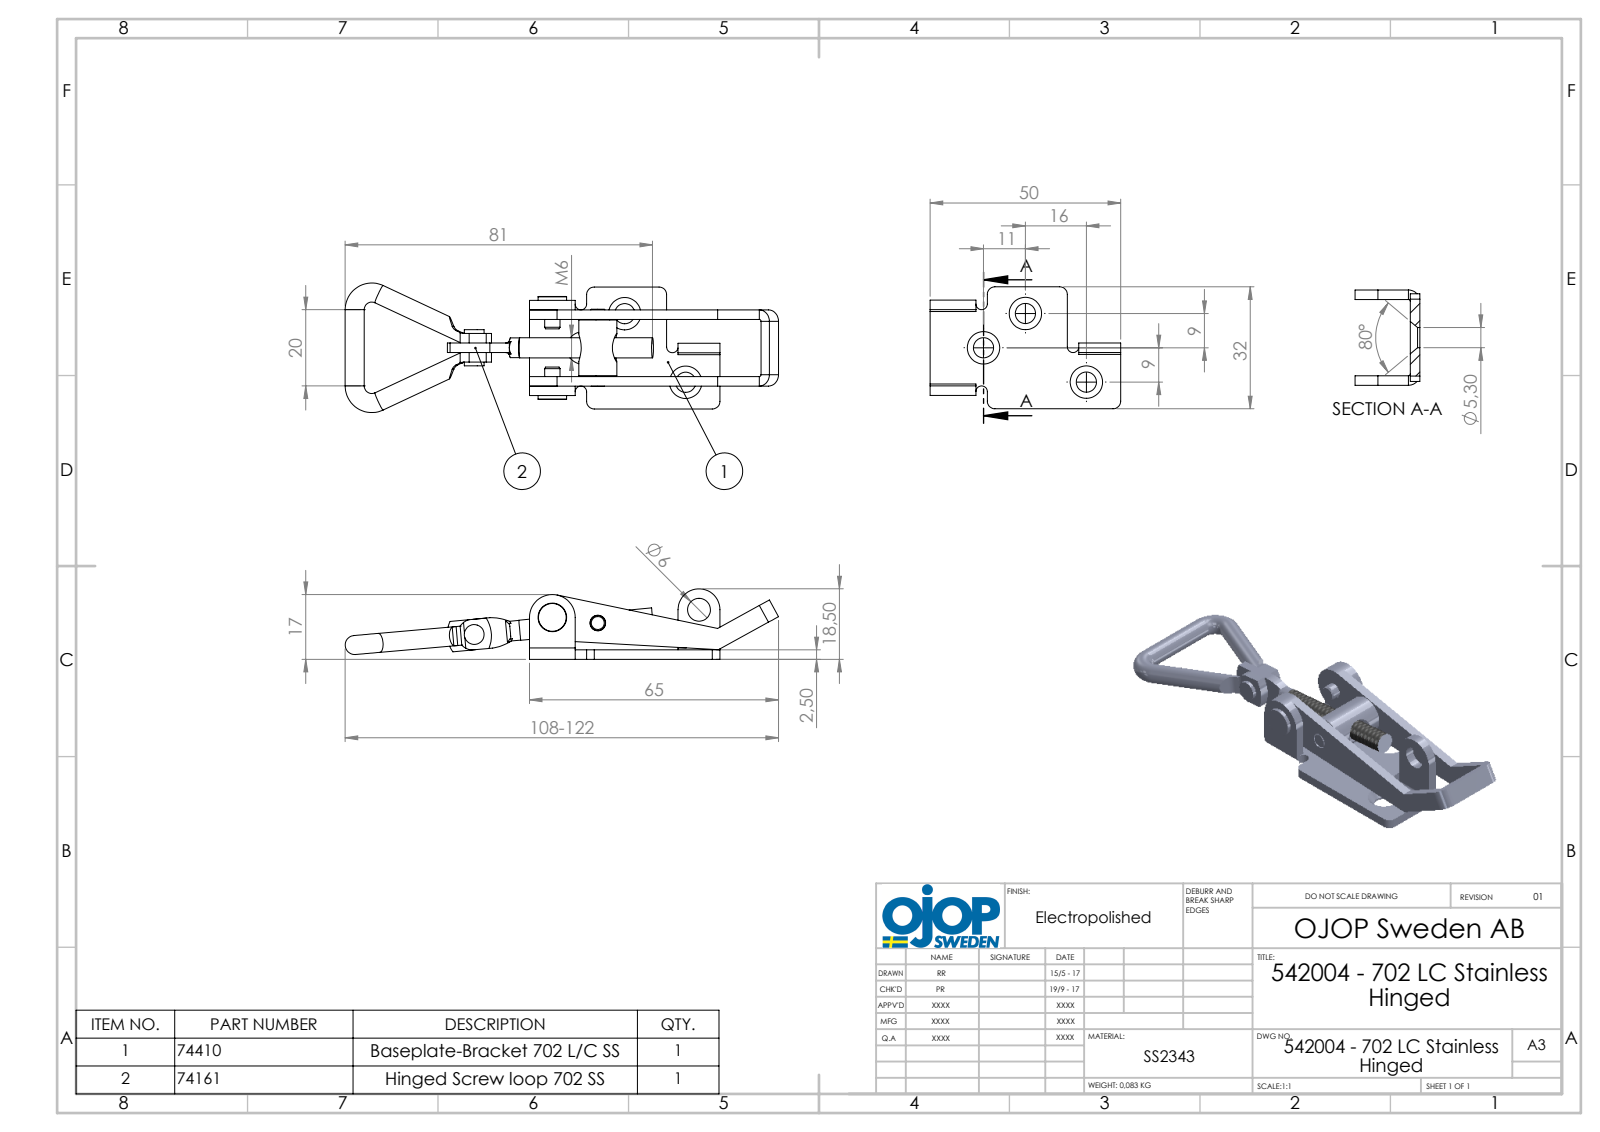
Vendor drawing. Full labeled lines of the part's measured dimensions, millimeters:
Part name (STEP PRODUCT): 702 - Ansatsnit; 702 - Skruv till ledad M6; 702 - Ring 702 M6; 702 - Rulle (+5 more)
STEP written by: SolidWorks 2015 (AUTOMOTIVE_DESIGN)
Units: millimetres
Bodies: 8 solids, 228 faces (90 planar, 110 cylindrical, 28 other)
Overall size (bounding box): 115.5 × 34 × 18.5
Volume: 10 978 mm³ · Surface area: 11 148 mm²
Round holes (diameter × count): ⌀4.1 ×3, ⌀5.3 ×3, ⌀6 ×2, ⌀5 ×1
Round bosses / shafts (diameter × count): ⌀5 ×3, ⌀4 ×2, ⌀10 ×1, ⌀7.5 ×1, ⌀5.3 ×1, ⌀5.2 ×1, ⌀5.18 ×1
Partial cylindrical surfaces — rounded edges, fillets, slot ends (radius × count): R2 ×8, R1 ×6, R0.5 ×5, R3 ×5, R1.5 ×2, R6.78 ×2, R12.31 ×2, R1.51 ×1
Main face-to-face distances: 2.5, 17.5, 20, 8.75, 11.25, 15, 5, 8.8, 8.7, 11.3
Hole centre spacings: 12.03, 14.21, 22.67, 24.08, 26.79, 28.46, 34.31, 38.55
